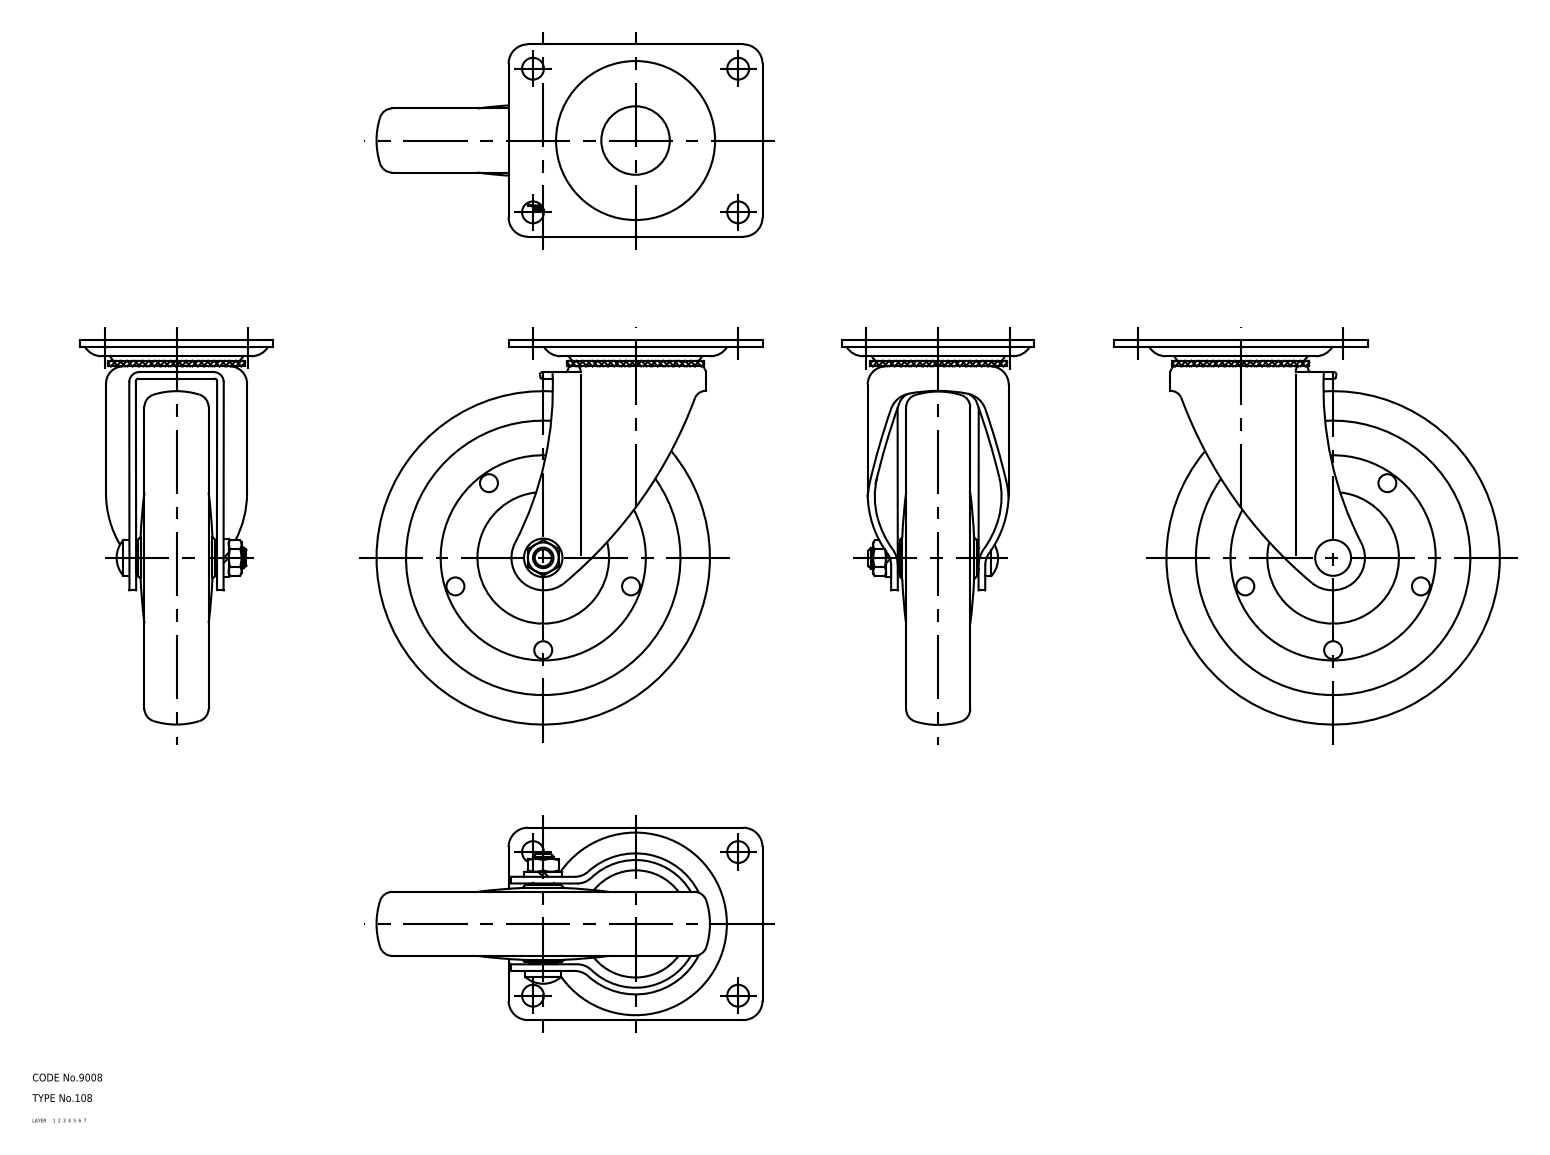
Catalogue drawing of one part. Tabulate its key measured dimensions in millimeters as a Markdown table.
| quantity | value |
| --- | --- |
| part name | wheel; mounting plate; main shaft; axle (+1 more) |
| STEP written by | CADfix (AUTOMOTIVE_DESIGN) |
| units | millimeters |
| bodies | 5 solids, 236 faces (0 planar, 0 cylindrical, 236 other) |
| overall size | 150.5 × 150 × 75 |
| volume | 365 736 mm³ |
| surface area | 80 837 mm² |
